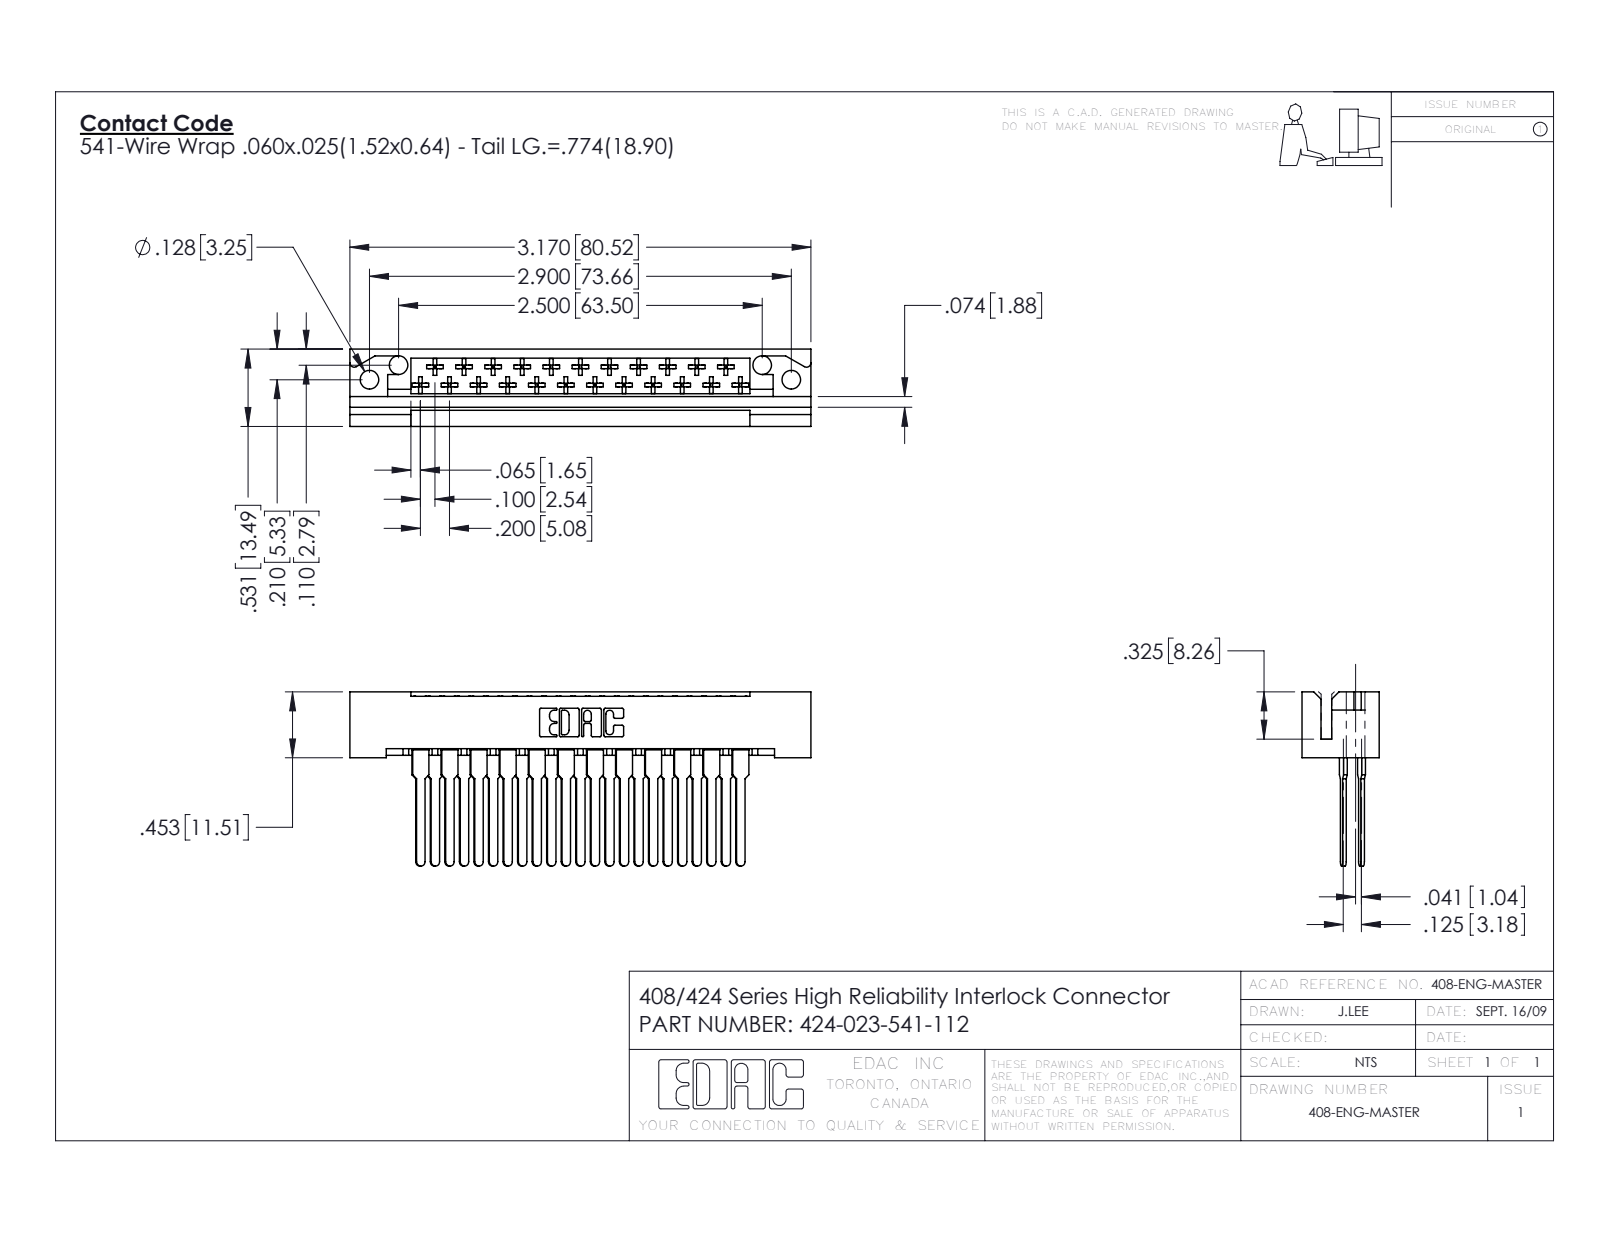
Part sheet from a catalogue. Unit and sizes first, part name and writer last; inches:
Units: inches
Overall size (bounding box): 3.17 × 1.197 × 0.531
Round holes (diameter × count): ⌀0.128 ×4
Partial cylindrical surfaces — rounded edges, fillets, slot ends (radius × count): R0.01 ×138, R0.02 ×25, R0.03 ×25, R0.01 ×22, R0.007 ×6, R0.031 ×6, R0.026 ×3
Main face-to-face distances: 0.4, 0.025, 0.531, 0.125, 0.1, 0.131, 0.326, 0.074, 0.205, 0.104
Hole centre spacings: 0.224, 2.702, 2.5, 2.9
Volume: 0.561 in³ · Surface area: 19.07 in²
Bodies: 24 solids, 1364 faces (1009 planar, 263 cylindrical, 92 other)
Part name (STEP PRODUCT): 408-290-001_408-290-141; 424-023-541-112; 424 Part_023
STEP written by: SolidWorks 2016 (CONFIG_CONTROL_DESIGN)
